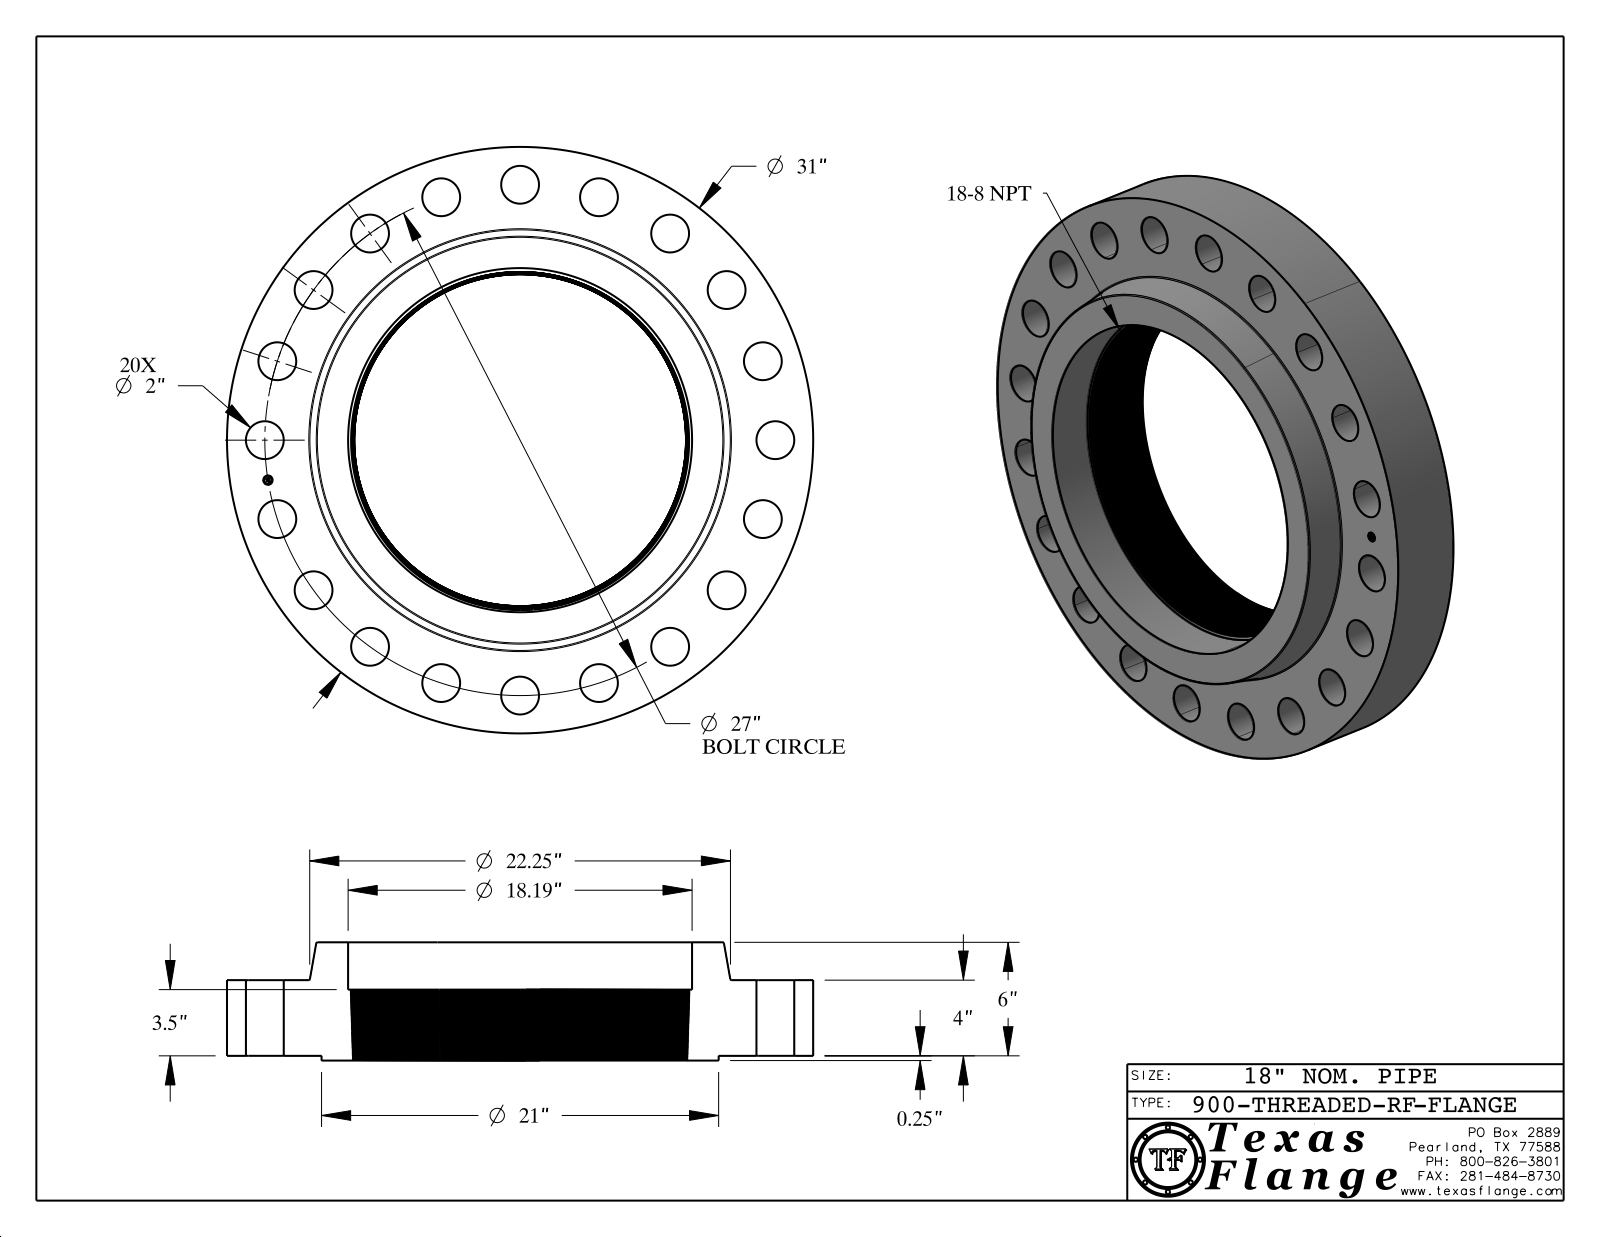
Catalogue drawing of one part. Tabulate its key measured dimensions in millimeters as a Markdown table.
| quantity | value |
| --- | --- |
| part name | 900-THREADED-RF |
| STEP written by | CATIA V5 STEP AP214 (AUTOMOTIVE_DESIGN) |
| units | millimeters |
| bodies | 1 solid, 749 faces (370 planar, 66 cylindrical, 313 other) |
| overall size | 787.4 × 787.4 × 158.8 |
| volume | 33 250 000 mm³ |
| surface area | 1 578 000 mm² |
| round holes (diameter × count) | 50.8 × 20, 12.6 × 1, 462 × 1 |
| round bosses / shafts (diameter × count) | 0.8 × 8, 787.4 × 1, 533.4 × 1, 9.9 × 1 |
| main face-to-face distances | 101.6, 6.4, 108, 158.8, 152.4, 50.8, 95.3, 88.9, 12.7, 63.5 |
| hole center spacings | 342.9, 554.8, 611, 652.2, 677.4, 107.3, 211.9, 311.4 |
